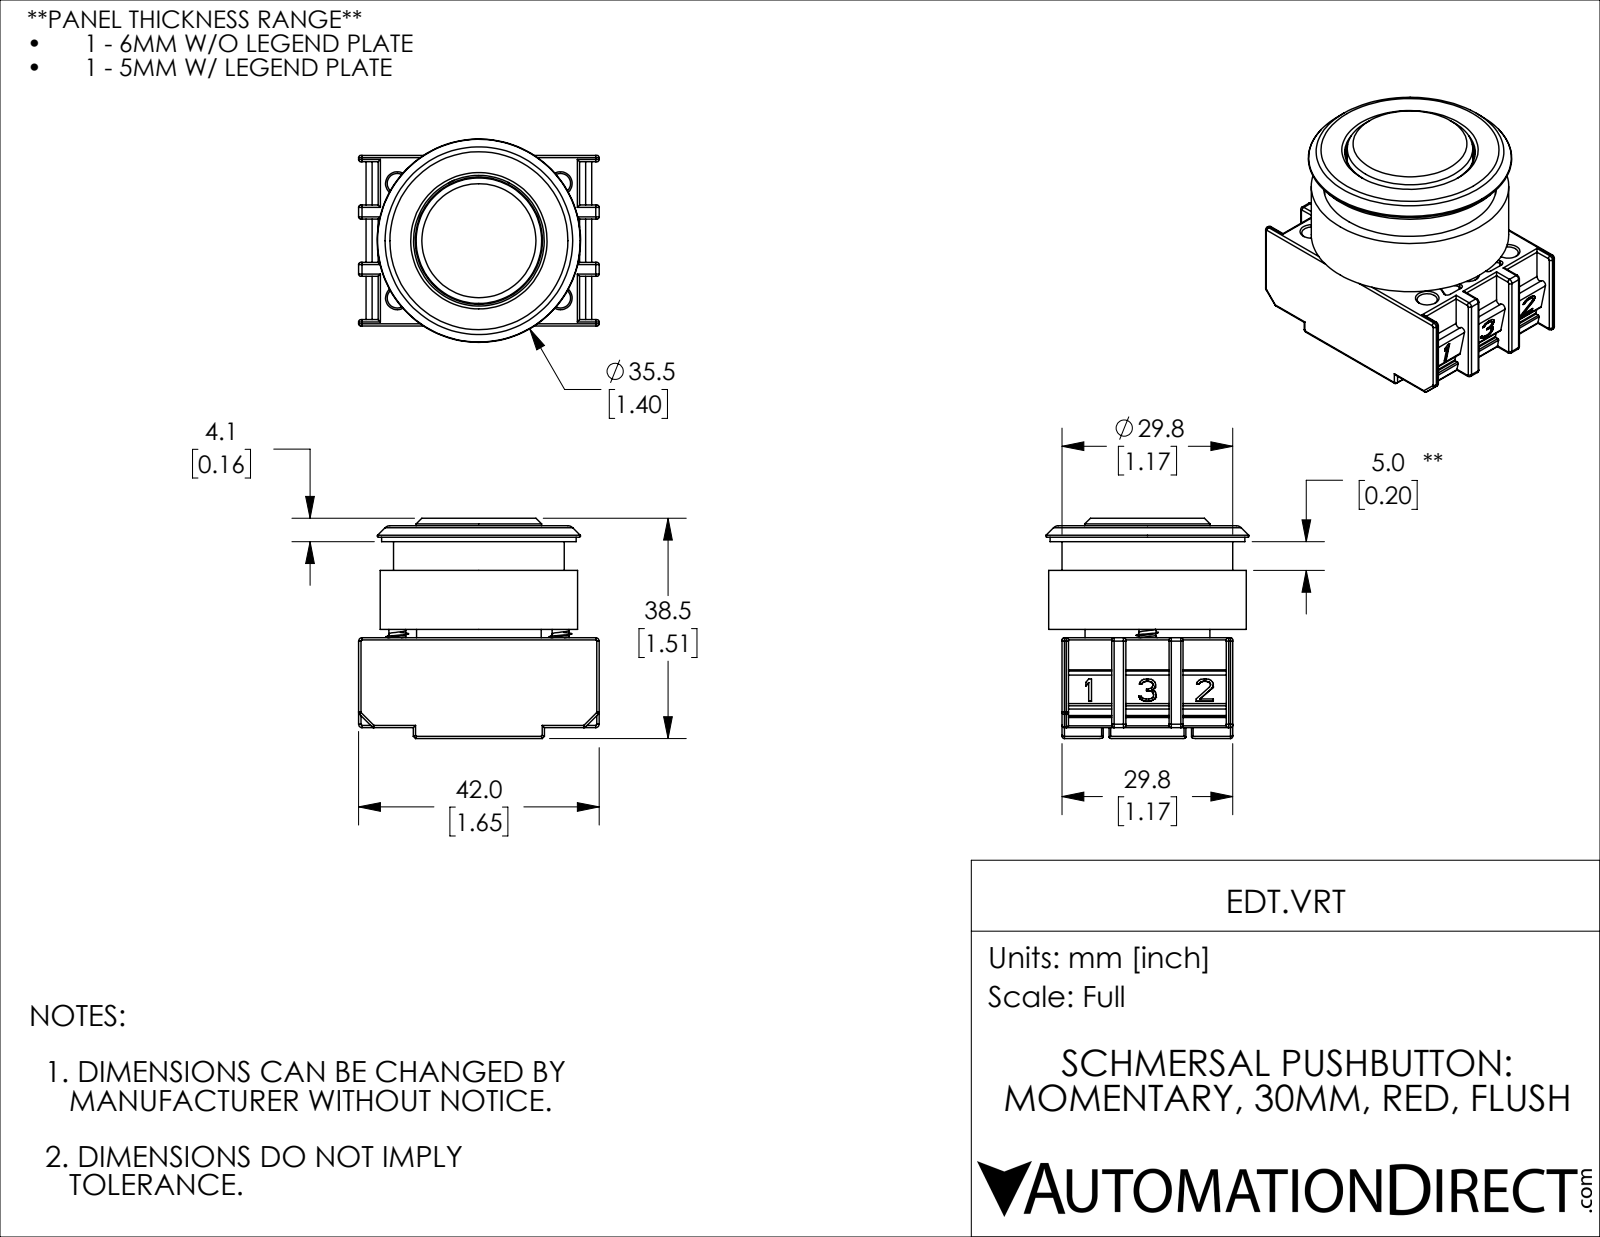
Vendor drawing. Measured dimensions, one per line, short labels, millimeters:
name: EDT.VRT
written by: SolidWorks 2019 (CONFIG_CONTROL_DESIGN)
unit: mm
bodies: 3 solids, 1361 faces (509 planar, 460 cylindrical, 392 other)
size: 42 × 38.45 × 35.5
volume: 22 602 mm³; area: 20 491 mm²
holes: 6× ⌀3.5, 6× ⌀5.15, 1× ⌀4.1, 1× ⌀12.5, 1× ⌀18, 1× ⌀19.2, 1× ⌀22.2, 1× ⌀22.8, 1× ⌀24.2, 1× ⌀26, 1× ⌀27, 1× ⌀30.2
bosses: 2× ⌀4.8, 2× ⌀2.93, 1× ⌀34.5, 1× ⌀34, 1× ⌀29.8, 1× ⌀24.6, 1× ⌀21.9, 1× ⌀21.8
rounds: 112× R0.4, 48× R0.3, 24× R0.2, 8× R0.6, 6× R0.5, 2× R0.1, 2× R0.6, 2× R0.8
face distances: 29.8, 1.9, 19.4, 5.9, 4.1, 1.45, 16.2, 19.05, 10, 1.3
hole spacings: 10, 17.41, 30.2, 28.5, 14.25, 20, 34.82
